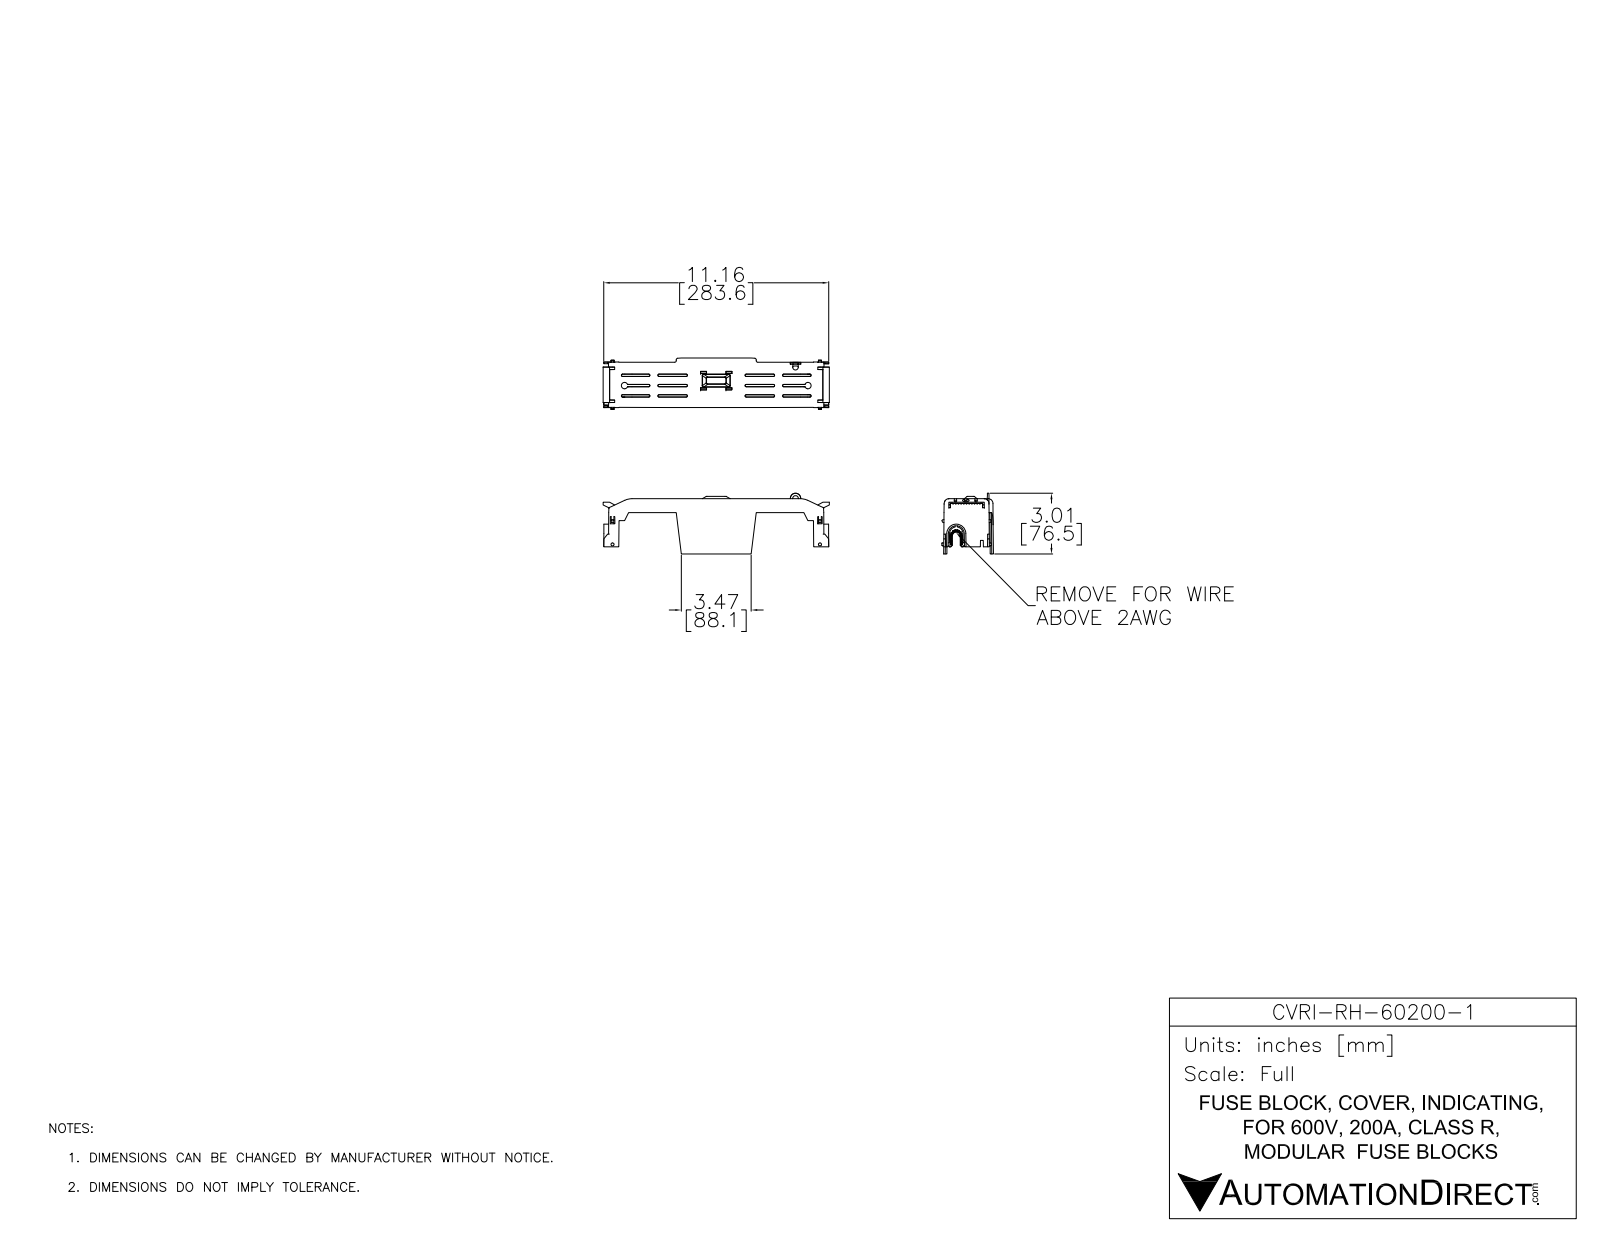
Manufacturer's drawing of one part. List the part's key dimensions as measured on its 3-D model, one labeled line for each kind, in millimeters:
Part name (STEP PRODUCT): CVRI-RH-60200-1
STEP written by: SolidWorks 2017 (AUTOMOTIVE_DESIGN)
Units: millimetres
Bodies: 1 solid, 1446 faces (937 planar, 106 cylindrical, 403 other)
Overall size (bounding box): 284.9 × 76.5 × 64.8
Volume: 90 180 mm³ · Surface area: 96 260 mm²
Round holes (diameter × count): ⌀7 ×1
Partial cylindrical surfaces — rounded edges, fillets, slot ends (radius × count): R1 ×16, R3 ×8, R4 ×7, R6 ×7, R2 ×6, R0.3 ×2, R0.5 ×2, R5 ×2
Main face-to-face distances: 2, 5, 3, 7, 13, 20.4, 15.8, 42.7, 44.7, 32.2
